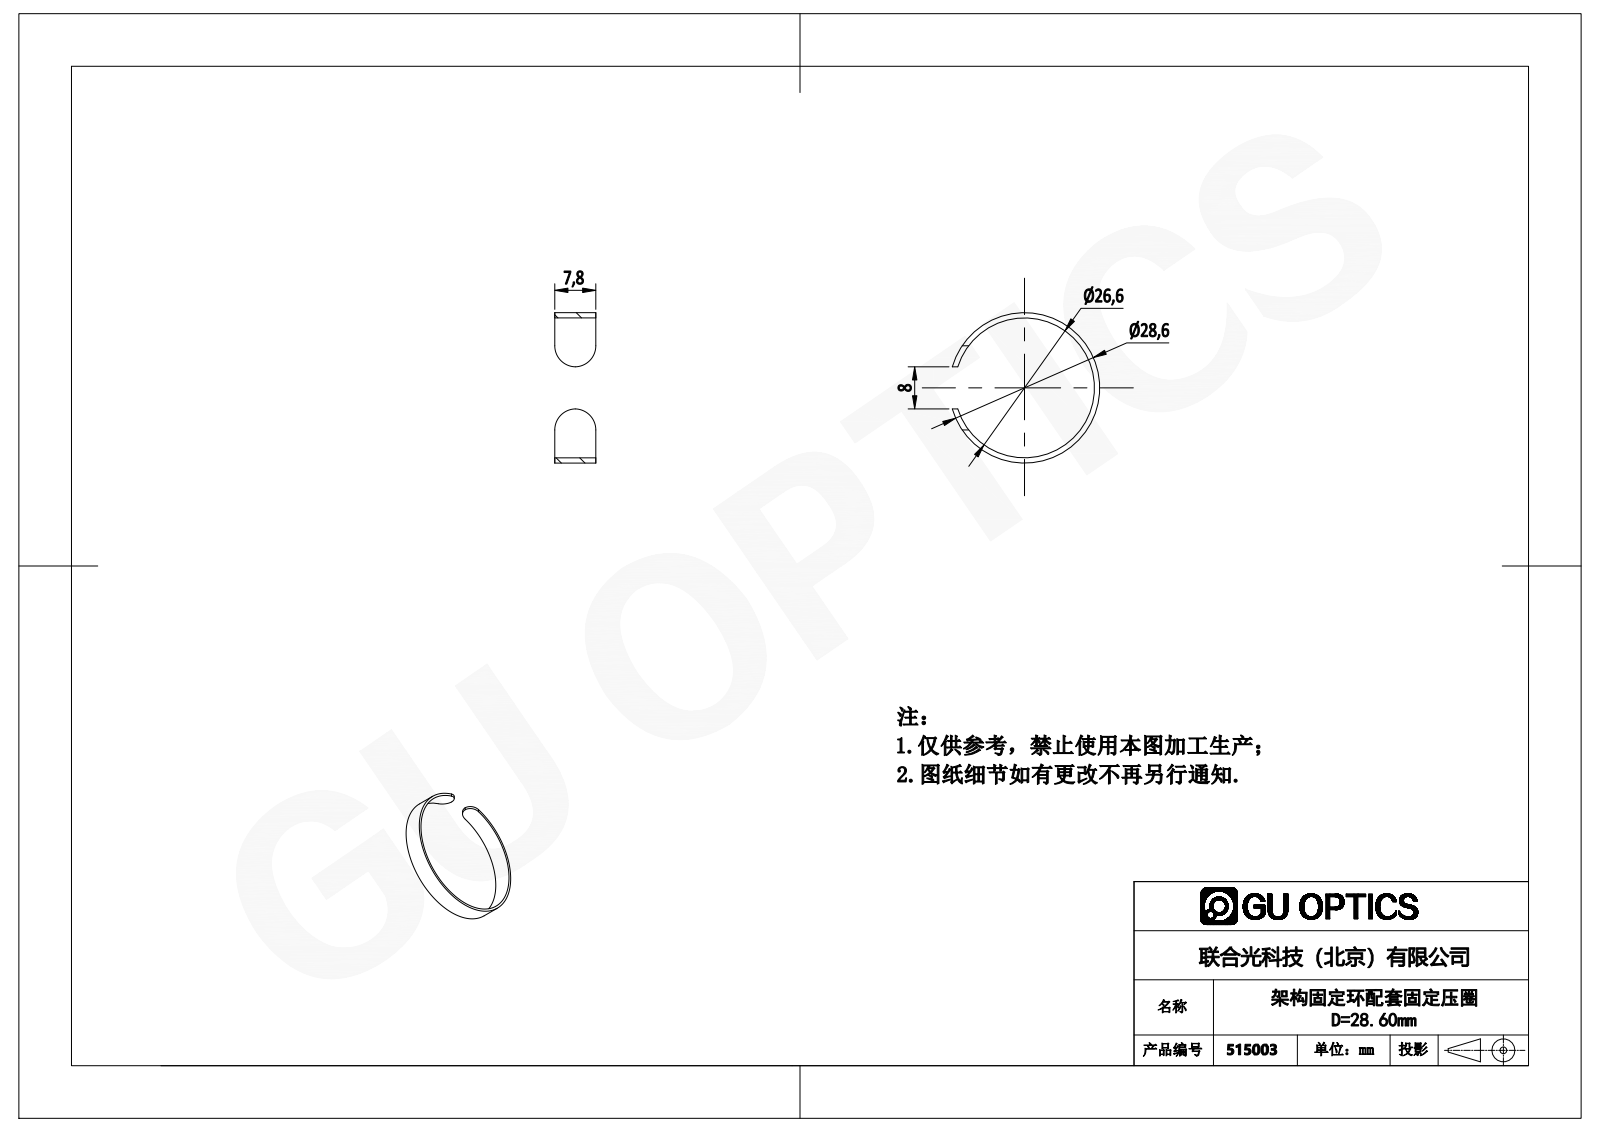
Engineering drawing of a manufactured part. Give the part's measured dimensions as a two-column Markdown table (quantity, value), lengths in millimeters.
| quantity | value |
| --- | --- |
| part name | 515003 |
| STEP written by | SolidWorks 2016 (CONFIG_CONTROL_DESIGN) |
| units | millimeters |
| bodies | 1 solid, 12 faces (2 planar, 10 cylindrical, 0 other) |
| overall size | 28.6 × 28.03 × 7.8 |
| volume | 598 mm³ |
| surface area | 1 363 mm² |
| round holes (diameter × count) | 26.6 × 1 |
| round bosses / shafts (diameter × count) | 28.6 × 1 |
| partial cylindrical surfaces (radius × count) | 4 × 4 |
| main face-to-face distances | 7.8 |
